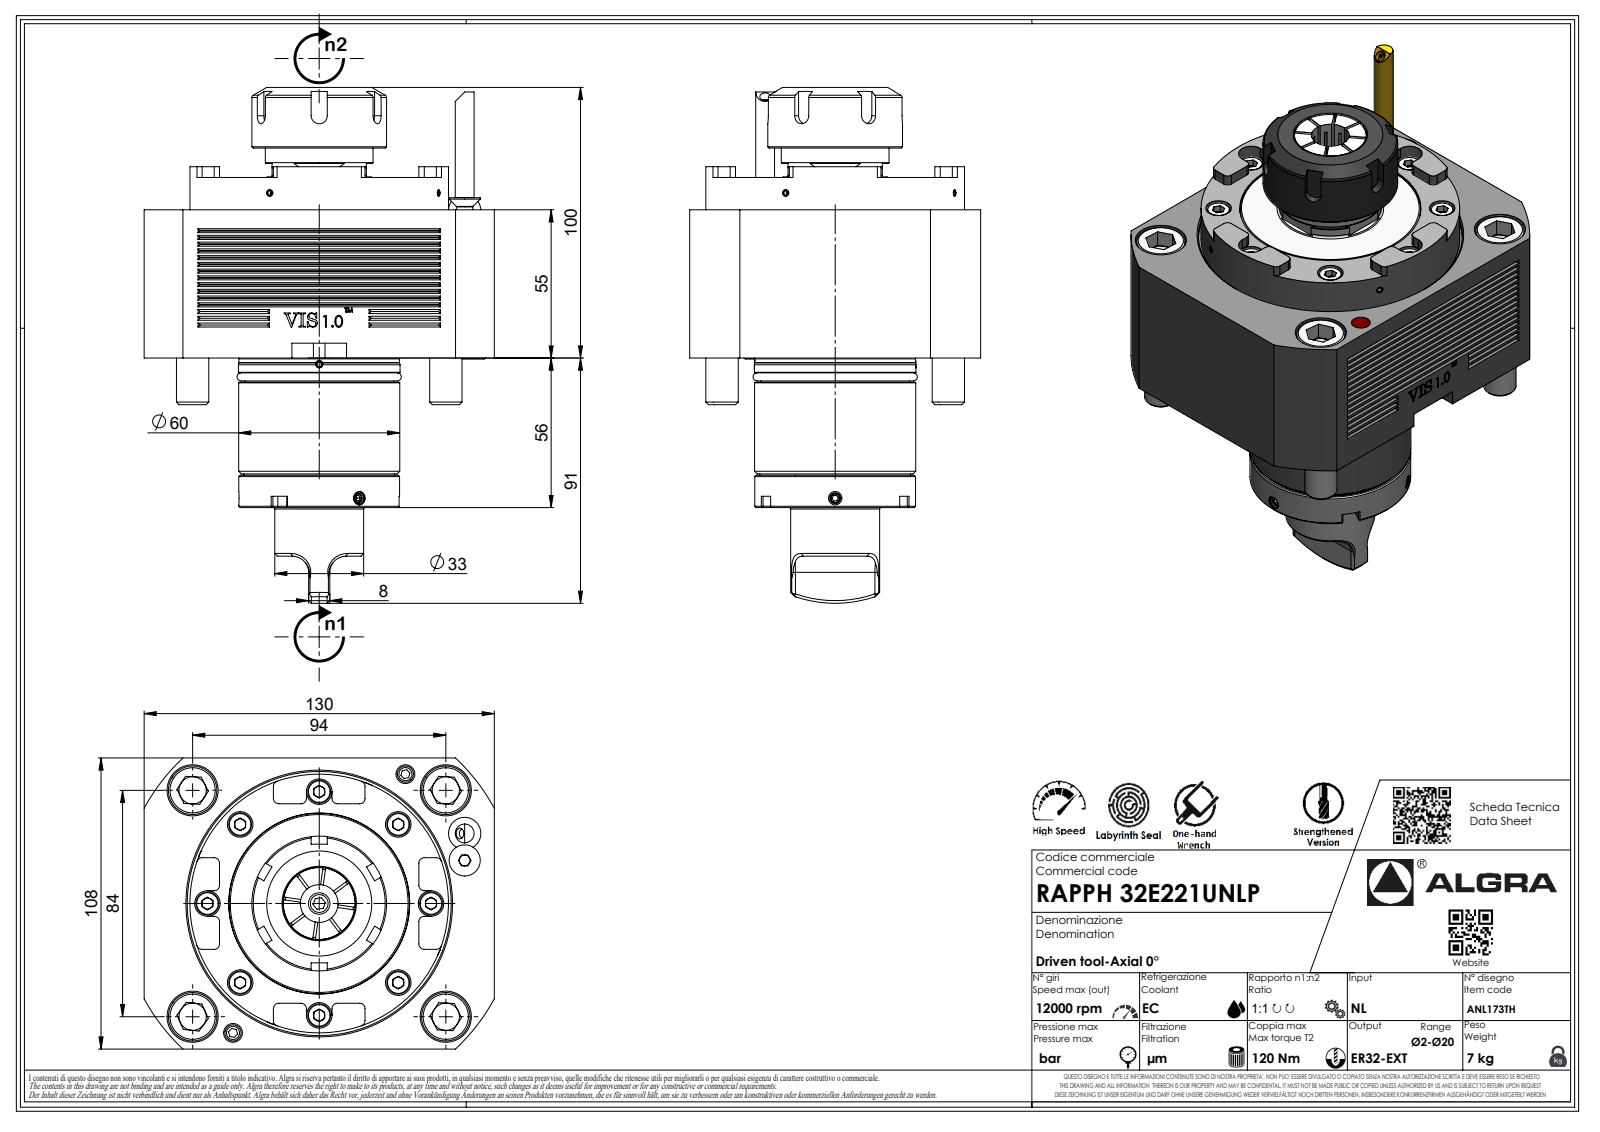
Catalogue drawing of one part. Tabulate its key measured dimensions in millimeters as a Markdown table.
| quantity | value |
| --- | --- |
| part name | RAPPH32E221UNLP |
| STEP written by | SolidWorks 2023 (AUTOMOTIVE_DESIGN) |
| units | millimeters |
| bodies | 1 solid, 511 faces (312 planar, 89 cylindrical, 110 other) |
| overall size | 191.41 × 130 × 108 |
| volume | 1 077 000 mm³ |
| surface area | 79 827 mm² |
| round holes (diameter × count) | 2.1 × 1, 4 × 1 |
| round bosses / shafts (diameter × count) | 12 × 4, 96 × 1, 60 × 1, 59.8 × 1, 50 × 1, 40 × 1, 33 × 1, 7 × 1 |
| partial cylindrical surfaces (radius × count) | 2 × 25, 0.33 × 7, 0.52 × 7, 3.7 × 7, 6 × 6, 4.75 × 4, 3 × 3, 0.21 × 1 |
| main face-to-face distances | 55, 108, 67, 12, 130, 55.5, 110.5, 122.5, 155.91, 100.41 |
